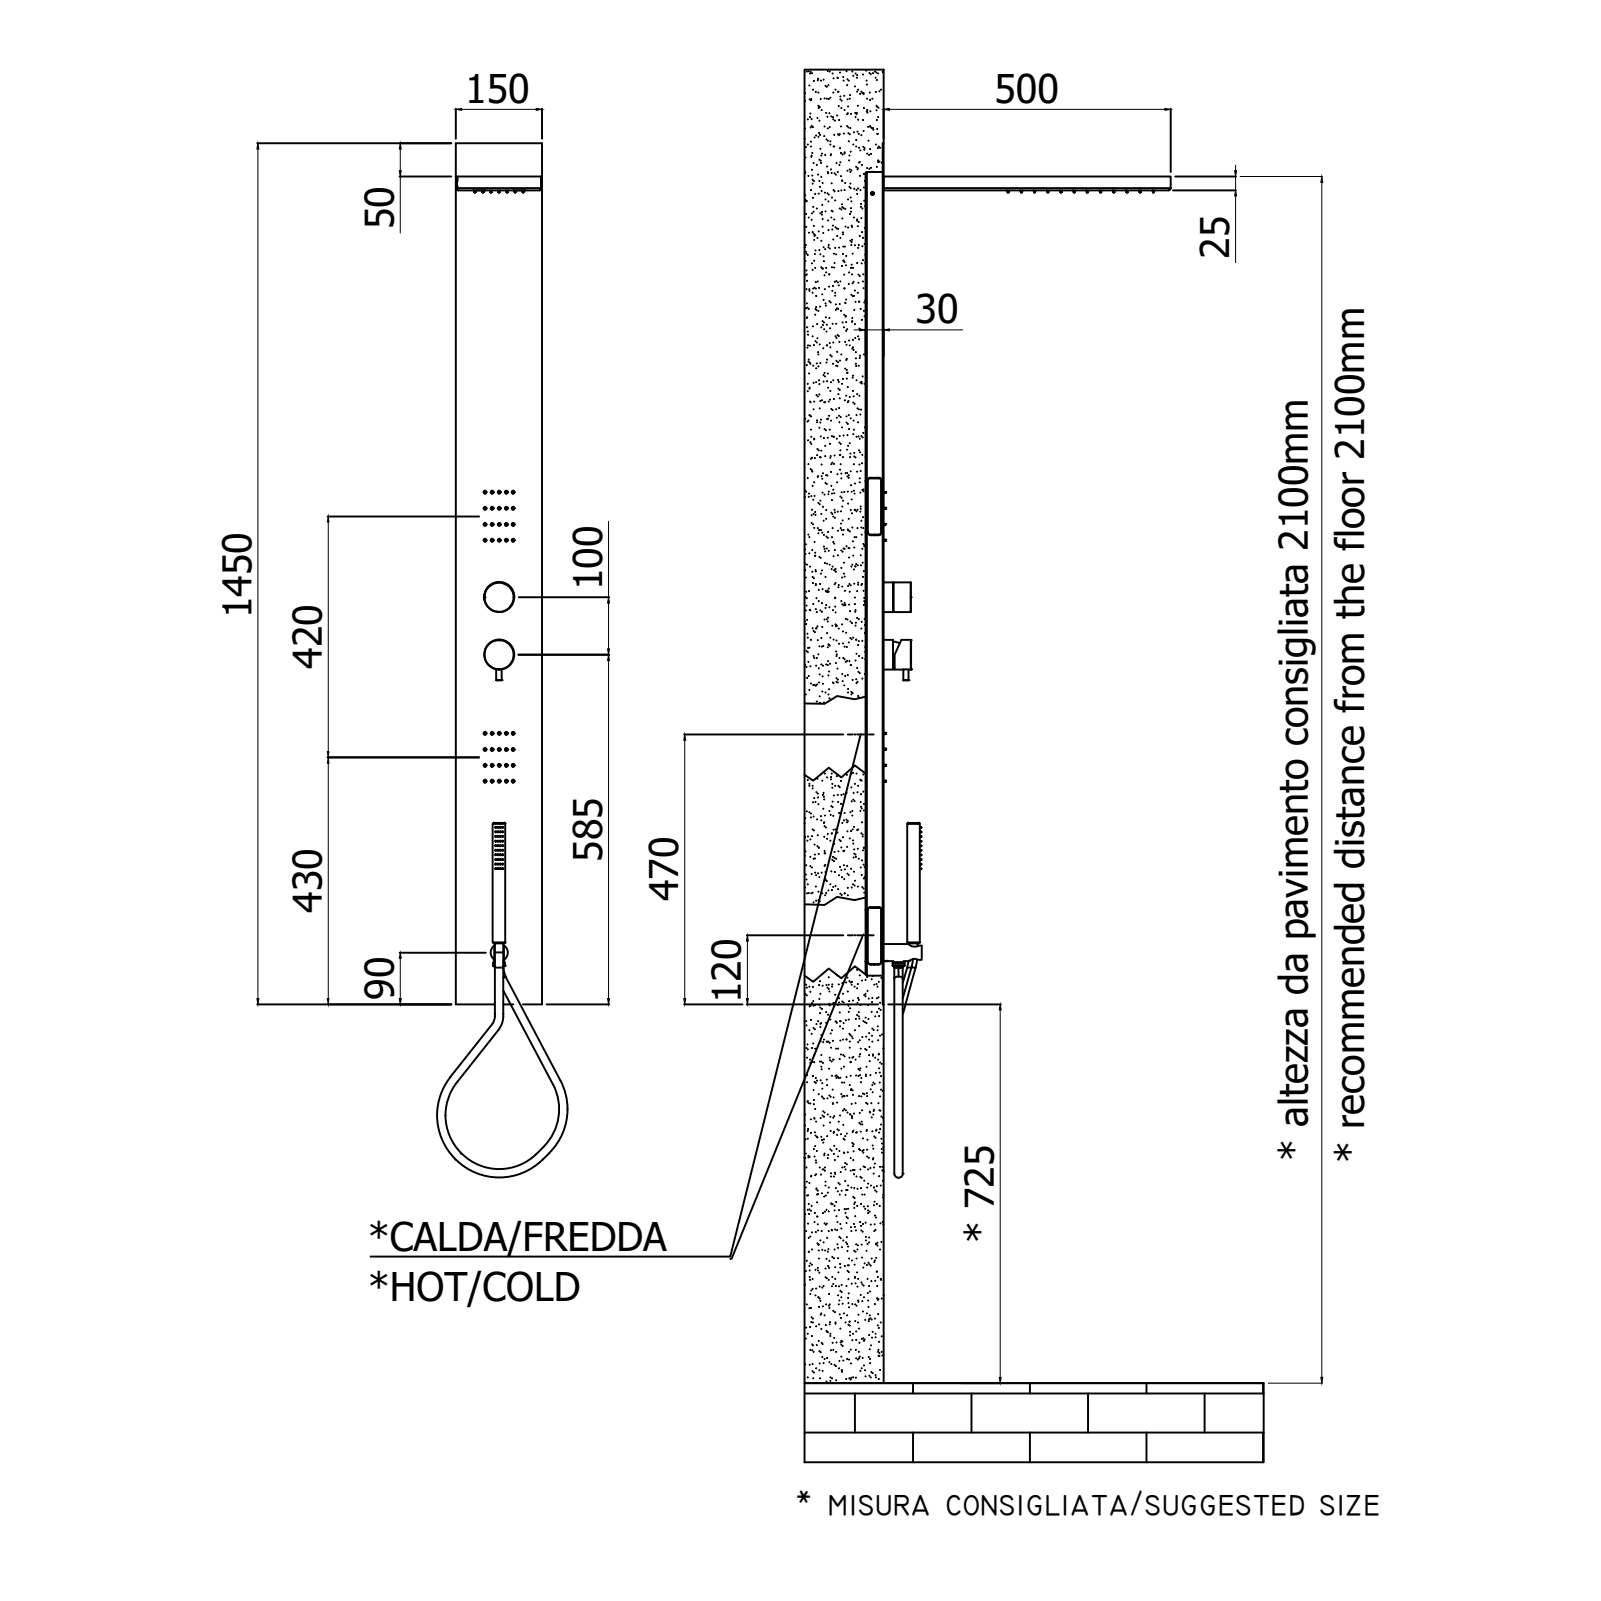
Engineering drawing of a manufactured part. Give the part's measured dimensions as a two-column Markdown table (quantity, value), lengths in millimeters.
| quantity | value |
| --- | --- |
| part name | ASSEM1-2091; S-00211_A_AF0; S-01003_A_AF0; S-01030_AF0 (+8 more) |
| STEP written by | CREO PARAMETRIC BY PTC INC, 2020044 (CONFIG_CONTROL_DESIGN) |
| units | millimeters |
| bodies | 172 solids, 10732 faces (2113 planar, 3901 cylindrical, 4718 other) |
| overall size | 1836.85 × 501.5 × 150 |
| volume | 1 059 000 mm³ |
| surface area | 1 224 000 mm² |
| round holes (diameter × count) | 1.5 × 116, 5 × 102, 1.7 × 84, 3.1 × 84, 5.2 × 16, 6.2 × 8, 2.5 × 7, 3.2 × 4, 3.3 × 4, 6 × 4, 10 × 3, 3 × 2 |
| round bosses / shafts (diameter × count) | 10 × 86, 3.3 × 84, 2 × 11, 6.7 × 4, 3.6 × 4, 3 × 4, 0.4 × 4, 51.8 × 3 |
| partial cylindrical surfaces (radius × count) | 0.26 × 624, 1.32 × 336, 0.1 × 99, 0.2 × 52, 0.96 × 48, 2 × 40, 1 × 32, 5.5 × 24 |
| main face-to-face distances | 1.5, 1, 21.5, 24, 22.5, 23, 3, 20.5, 17.5, 2.5 |
| hole center spacings | 420.18, 23, 27.74, 55.5, 46, 26.93, 48.08, 69 |
